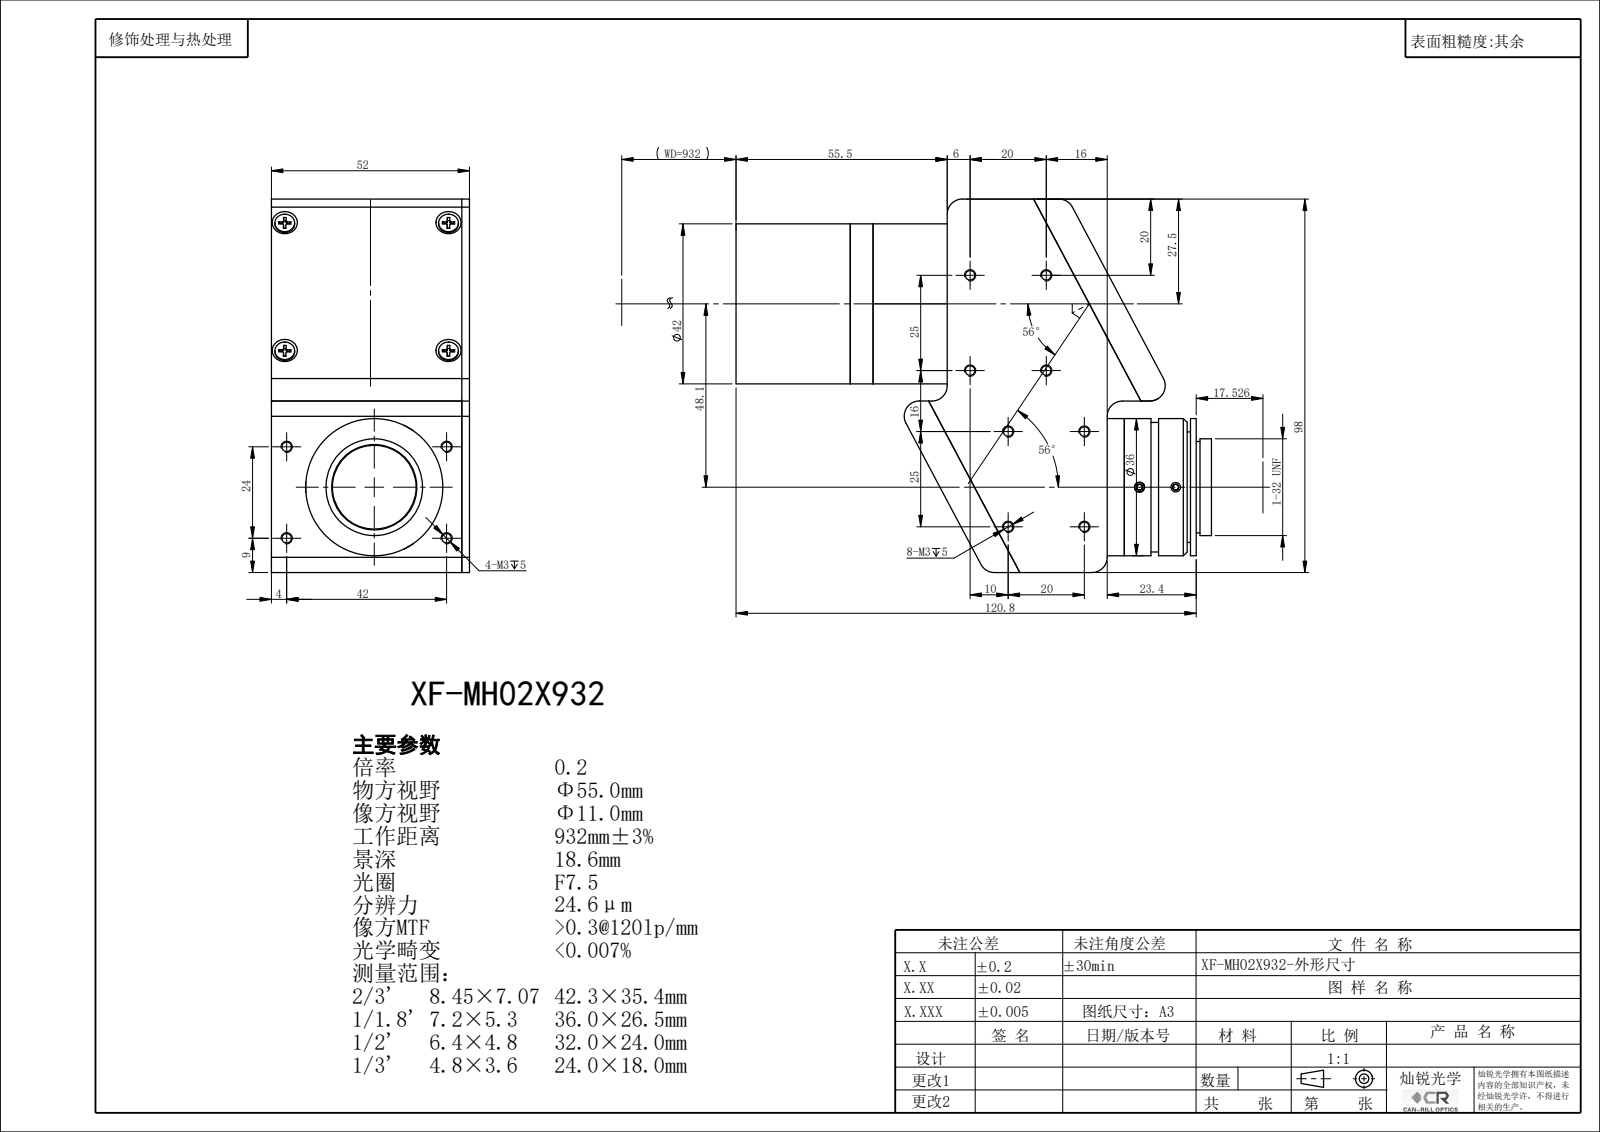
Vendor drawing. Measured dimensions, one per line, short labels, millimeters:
name: XF-MH02X932
written by: SolidWorks 2022 (CONFIG_CONTROL_DESIGN)
unit: mm
bodies: 0 solids, 443 faces (243 planar, 152 cylindrical, 48 other)
size: 124.85 × 98 × 52
holes: 15× ⌀2.5, 1× ⌀22.4, 1× ⌀24, 1× ⌀26.4, 1× ⌀33, 1× ⌀36.4
bosses: 8× ⌀5.2, 6× ⌀3.5, 1× ⌀42, 1× ⌀36, 1× ⌀34, 1× ⌀25.4
rounds: 47× R0.3, 11× R4
face distances: 52, 65.19, 98, 57.2, 7.99, 42, 8, 49.2, 57.19, 10.5
hole spacings: 42.2, 20, 25, 32.02, 18.87, 66.75, 24, 42
